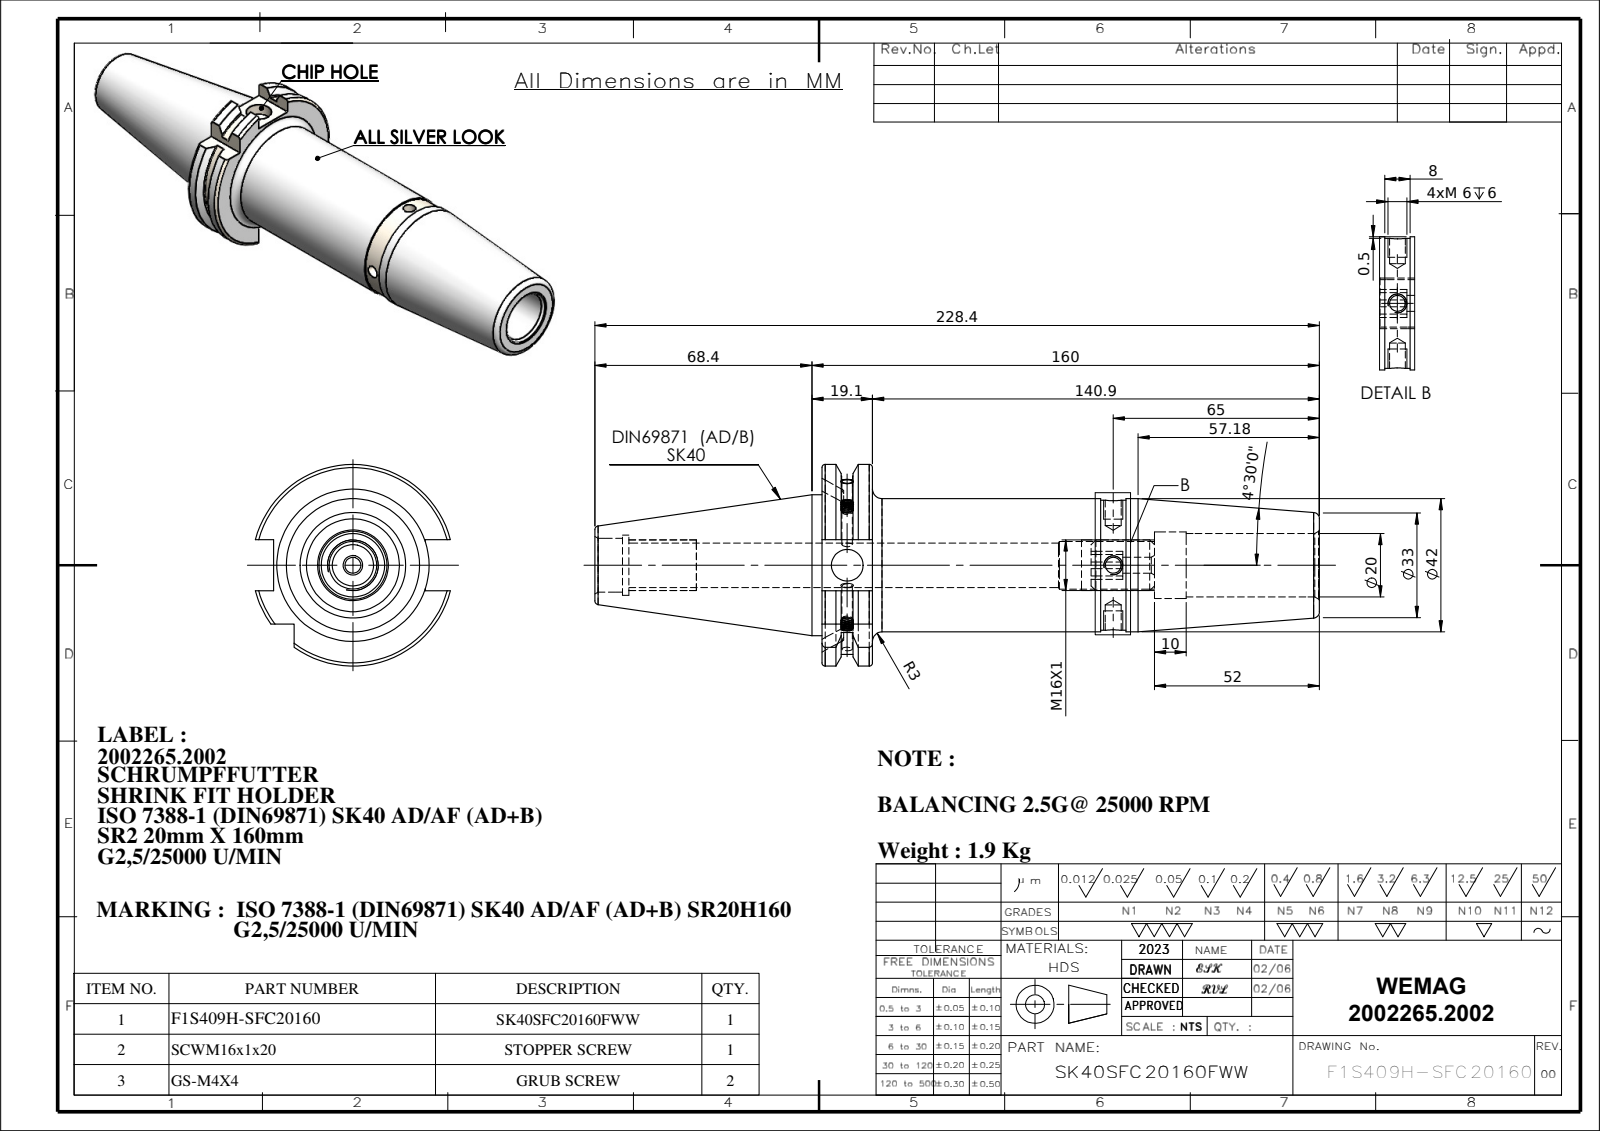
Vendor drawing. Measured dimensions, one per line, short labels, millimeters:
name: GS-M4X4_DIN 913 - M4 x 4-N; SK40SFC20160FWW; SCWM16X1P; 91406-SR220160
written by: SolidWorks 2018 (CONFIG_CONTROL_DESIGN)
unit: mm
bodies: 4 solids, 238 faces (60 planar, 70 cylindrical, 108 other)
size: 228.4 × 63.55 × 61.48
volume: 248 932 mm³; area: 48 146 mm²
holes: 3× ⌀5, 1× ⌀3.3, 1× ⌀10, 1× ⌀14, 1× ⌀15, 1× ⌀17, 1× ⌀19, 1× ⌀19.99, 1× ⌀20.99
bosses: 2× ⌀4, 1× ⌀44.45, 1× ⌀42, 1× ⌀41, 1× ⌀16
rounds: 1× R28.12, 1× R31.77
face distances: 15.9, 156.8, 140.9, 104.8, 88.9, 52, 16.1, 47.8, 8, 71.6
hole spacings: 83.85
